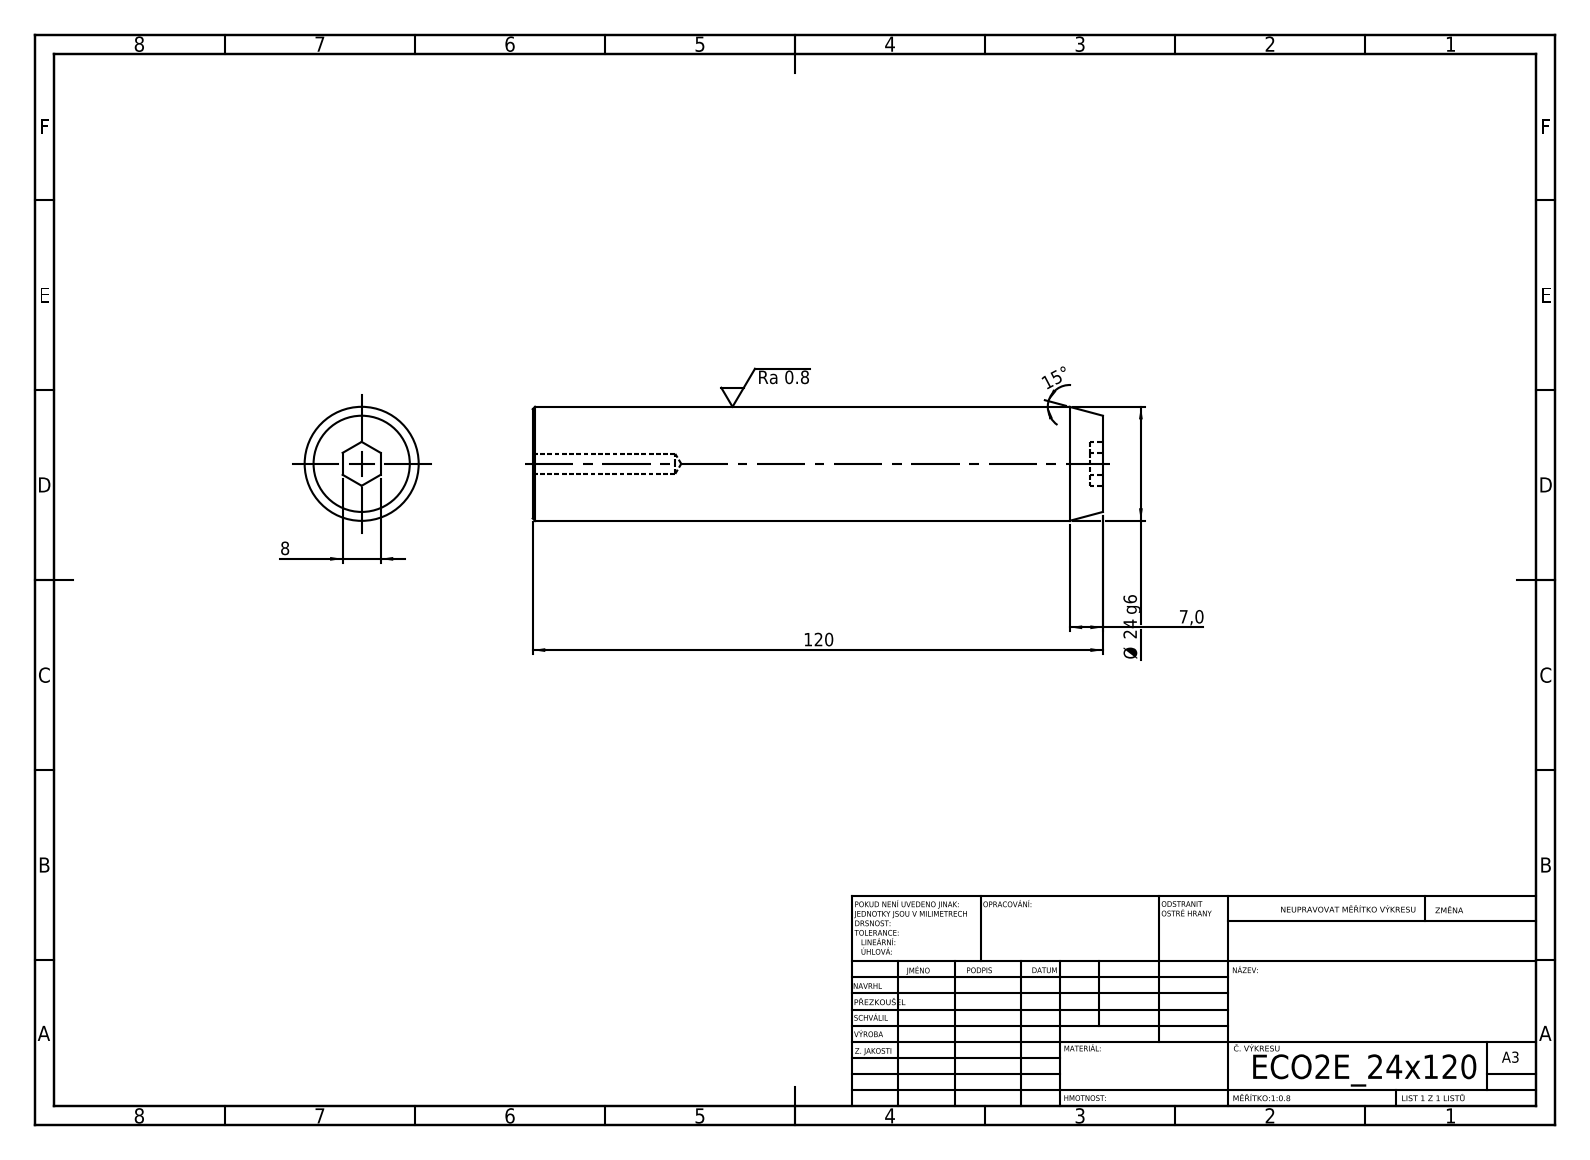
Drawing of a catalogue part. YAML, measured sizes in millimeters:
step_written_by: "SolidWorks 2019 (CONFIG_CONTROL_DESIGN)"
units: millimeters
bodies: {solids: 1, faces: 19, planar: 9, cylindrical: 4, other: 6}
overall_size: [120, 24, 24]
volume: 53232
surface_area: 10251
round_holes:
  - {diameter: 4.2, count: 1}
round_bosses_or_shafts:
  - {diameter: 24, count: 1}
face_to_face_distances: [120, 2.8, 117.2, 8]
